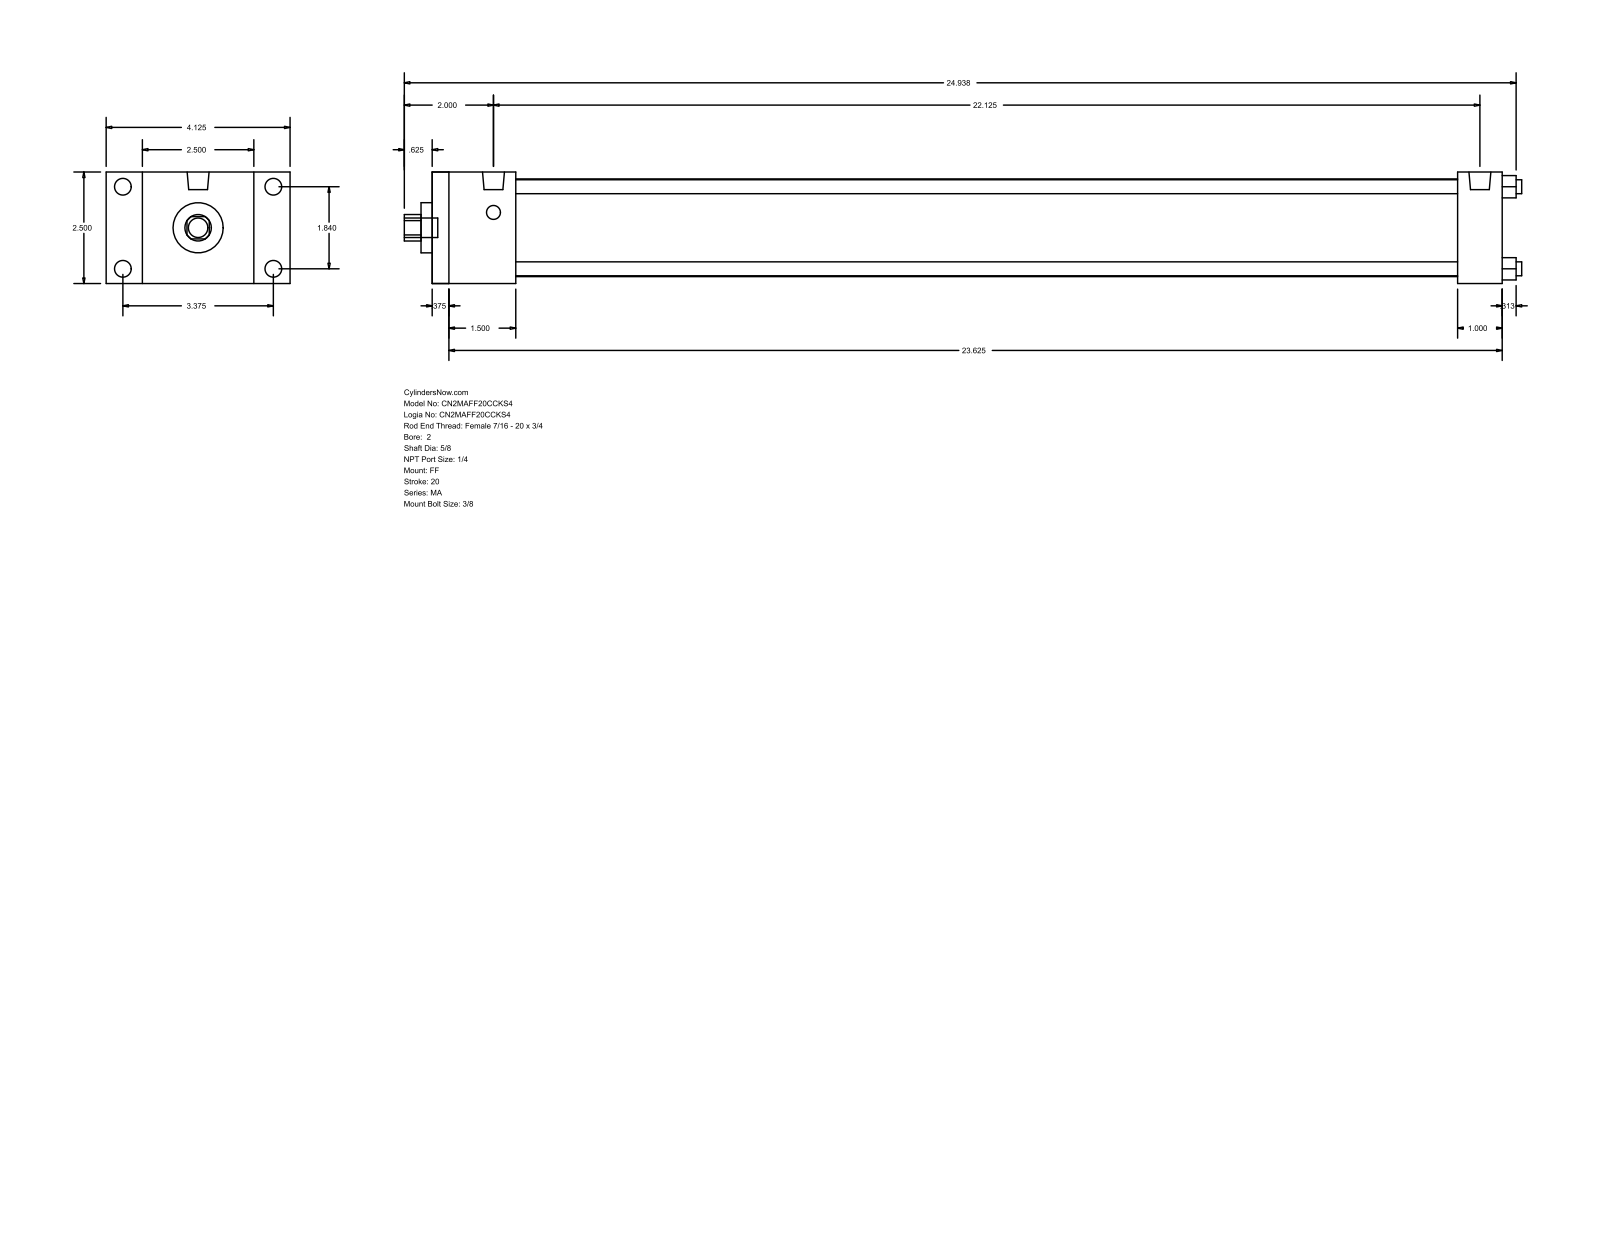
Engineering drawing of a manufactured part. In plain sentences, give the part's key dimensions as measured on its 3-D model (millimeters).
The part is named "MA_FF__0200_0.625". Its 3-D file was written by "GSSL Pune (CONFIG_CONTROL_DESIGN)". It is 0 solids with 92 faces: 64 planar, 28 cylindrical and 0 other. Overall it measures 636.59 by 104.78 by 63.5 millimeters. Round holes: 4 of diameter 7.94, 1 of diameter 15.88, 1 of diameter 28.57, 1 of diameter 55.63. Round bosses or shafts: 4 of diameter 9.53, 4 of diameter 7.94, 2 of diameter 12.49, 1 of diameter 11.11. Partial cylindrical surfaces (rounded edges, fillets, slot ends): 1 of radius 7.54. The main face-to-face distances are 63.5, 609.6, 9.52, 600.08, 25.4, 38.1, 47.62, 584.2, 574.68, 536.58. The hole center spacings are 33.05, 46.74, 66.1.
